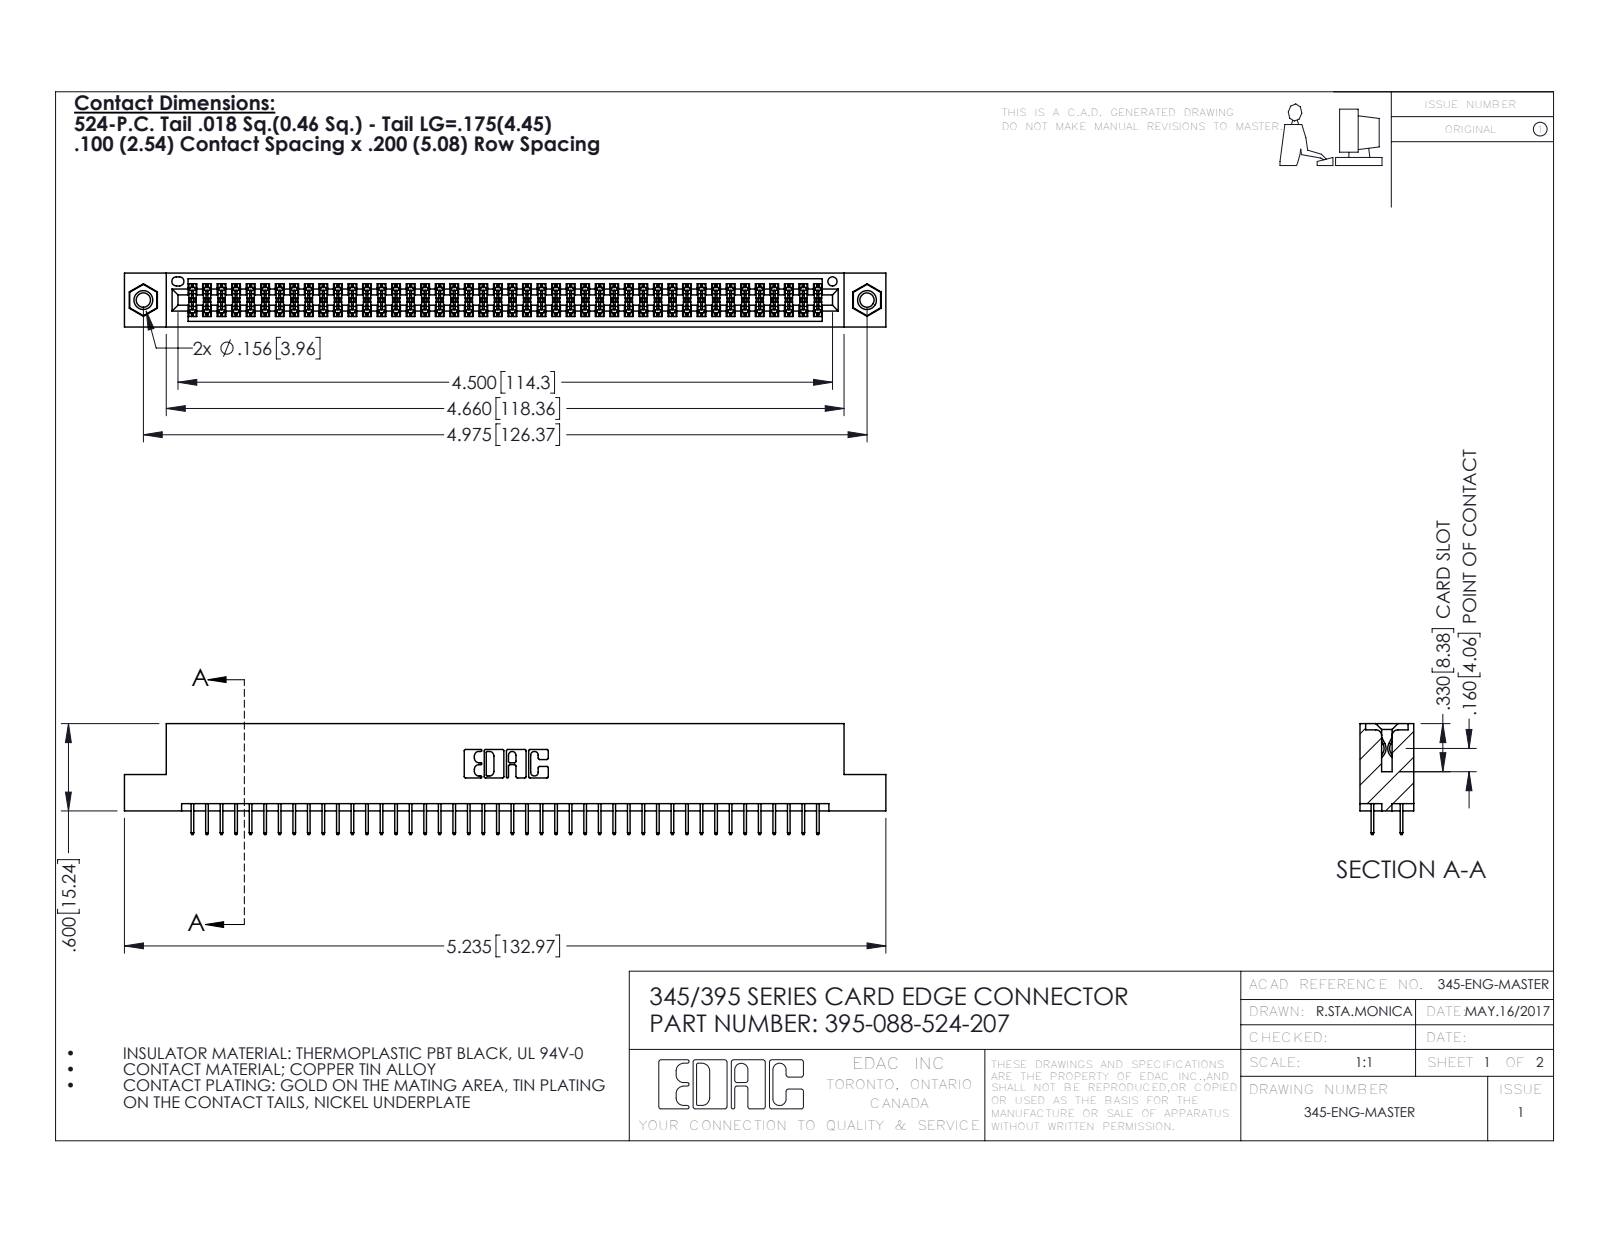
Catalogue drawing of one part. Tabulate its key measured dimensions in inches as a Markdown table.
| quantity | value |
| --- | --- |
| part name | 395-088-524-207; 345-250-001_345-250-005-103; 345 Part_Flush Mounting Lugs - 0.156 Dia-TI; 345-292-001_345-293-124 |
| STEP written by | SolidWorks 2016 (CONFIG_CONTROL_DESIGN) |
| units | inches |
| bodies | 91 solids, 4938 faces (3544 planar, 1378 cylindrical, 16 other) |
| overall size | 5.235 × 0.762 × 0.37 |
| volume | 0.78 in³ |
| surface area | 28.86 in² |
| round holes (diameter × count) | 0.098 × 2, 0.125 × 2, 0.156 × 2, 0.064 × 1 |
| round bosses / shafts (diameter × count) | 0.155 × 2 |
| partial cylindrical surfaces (radius × count) | 0.006 × 132, 0.01 × 22, 0.007 × 6, 0.031 × 6, 0.026 × 3, 0.014 × 2, 0.019 × 2, 0.022 × 2 |
| main face-to-face distances | 0.072, 0.298, 0.2, 0.37, 0.098, 0.272, 0.025, 0.225, 0.072, 0.175 |
| hole center spacings | 0.27, 4.739, 4.975 |
